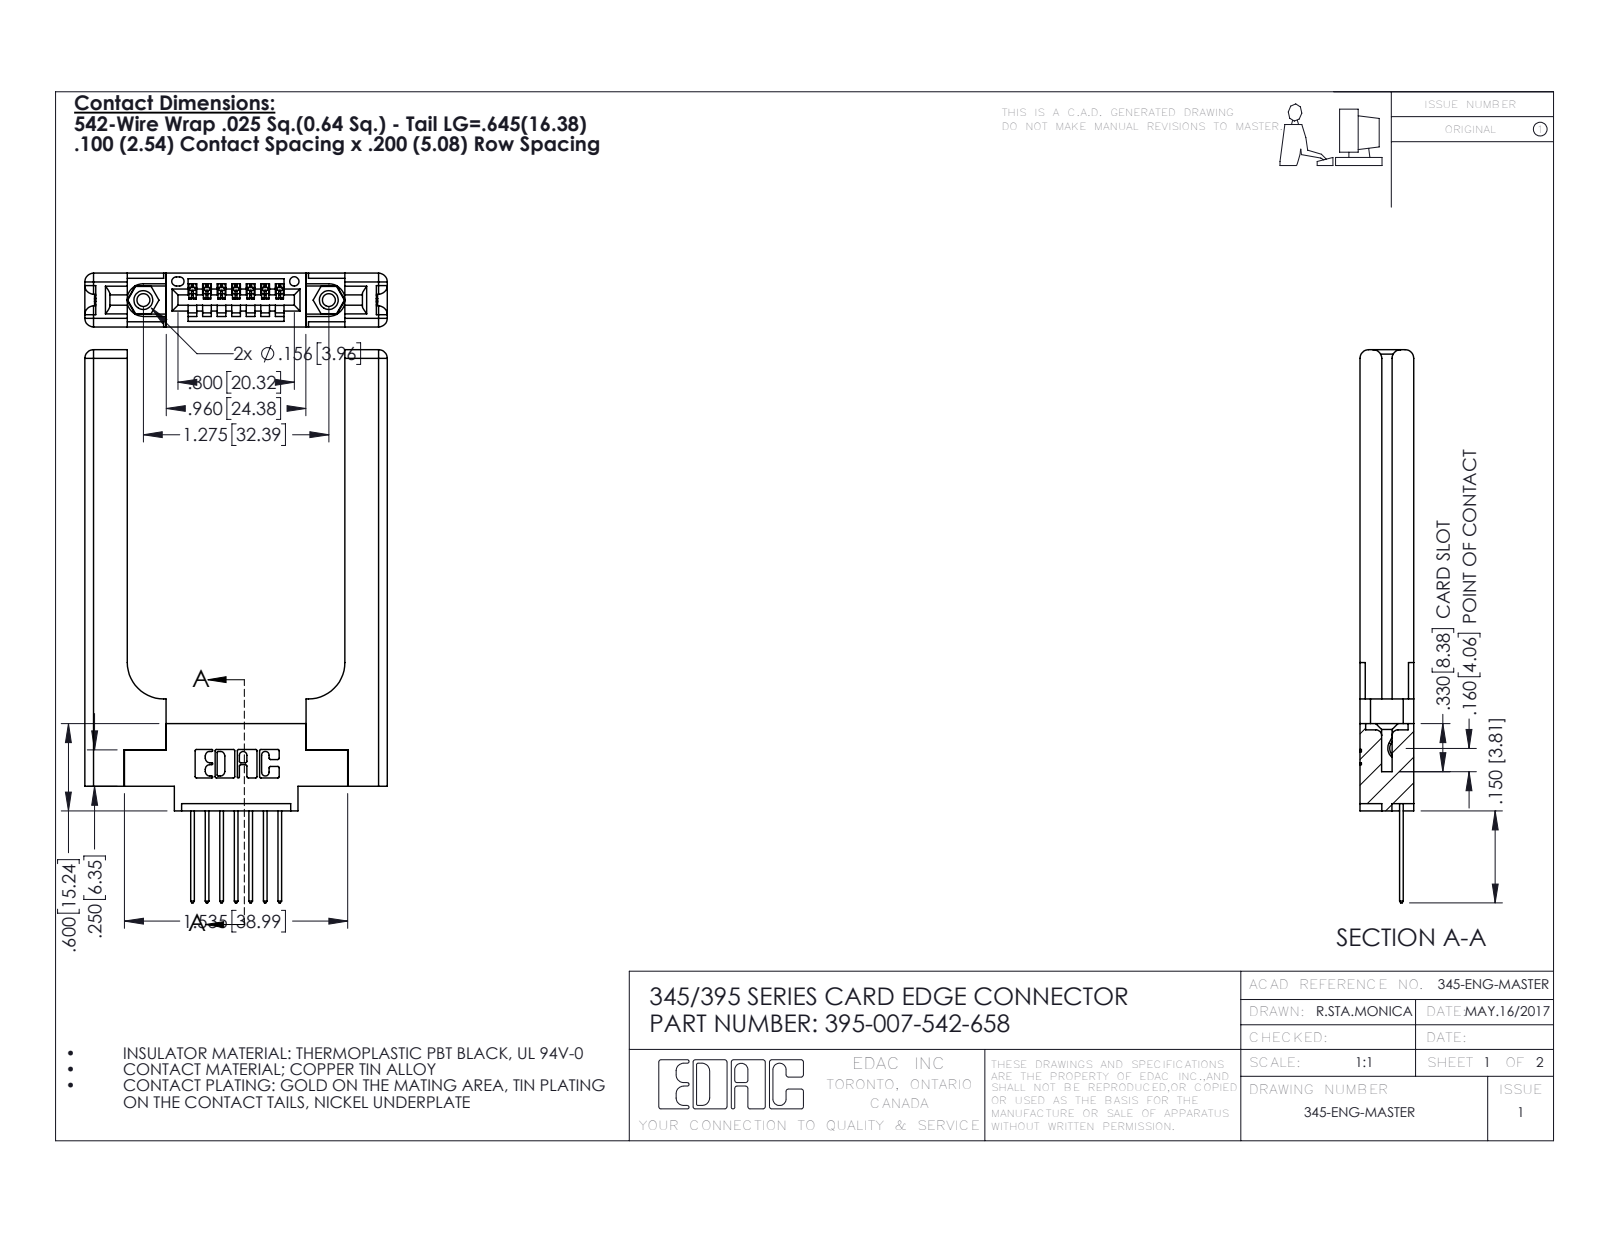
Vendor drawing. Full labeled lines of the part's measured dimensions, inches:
Part name (STEP PRODUCT): 345-292-001_345-293-142; 345 Part_0.170 Offset - 0.156 Dia-TH; 395-007-542-658; 345-250-001_345-250-001-102 (+1 more)
STEP written by: SolidWorks 2016 (CONFIG_CONTROL_DESIGN)
Units: inches
Bodies: 12 solids, 792 faces (512 planar, 220 cylindrical, 60 other)
Overall size (bounding box): 3.802 × 2.079 × 0.37
Volume: 0.802 in³ · Surface area: 17.37 in²
Round holes (diameter × count): ⌀0.089 ×2, ⌀0.125 ×2, ⌀0.156 ×2, ⌀0.064 ×1
Round bosses / shafts (diameter × count): ⌀0.155 ×2
Partial cylindrical surfaces — rounded edges, fillets, slot ends (radius × count): R0.01 ×22, R0.06 ×16, R0.006 ×14, R0.01 ×14, R0.007 ×6, R0.031 ×6, R0.026 ×3, R0.03 ×2
Main face-to-face distances: 0.37, 0.15, 0.22, 0.072, 0.077, 0.148, 0.298, 1.496, 0.071, 0.12
Hole centre spacings: 0.27, 1.045, 1.275
